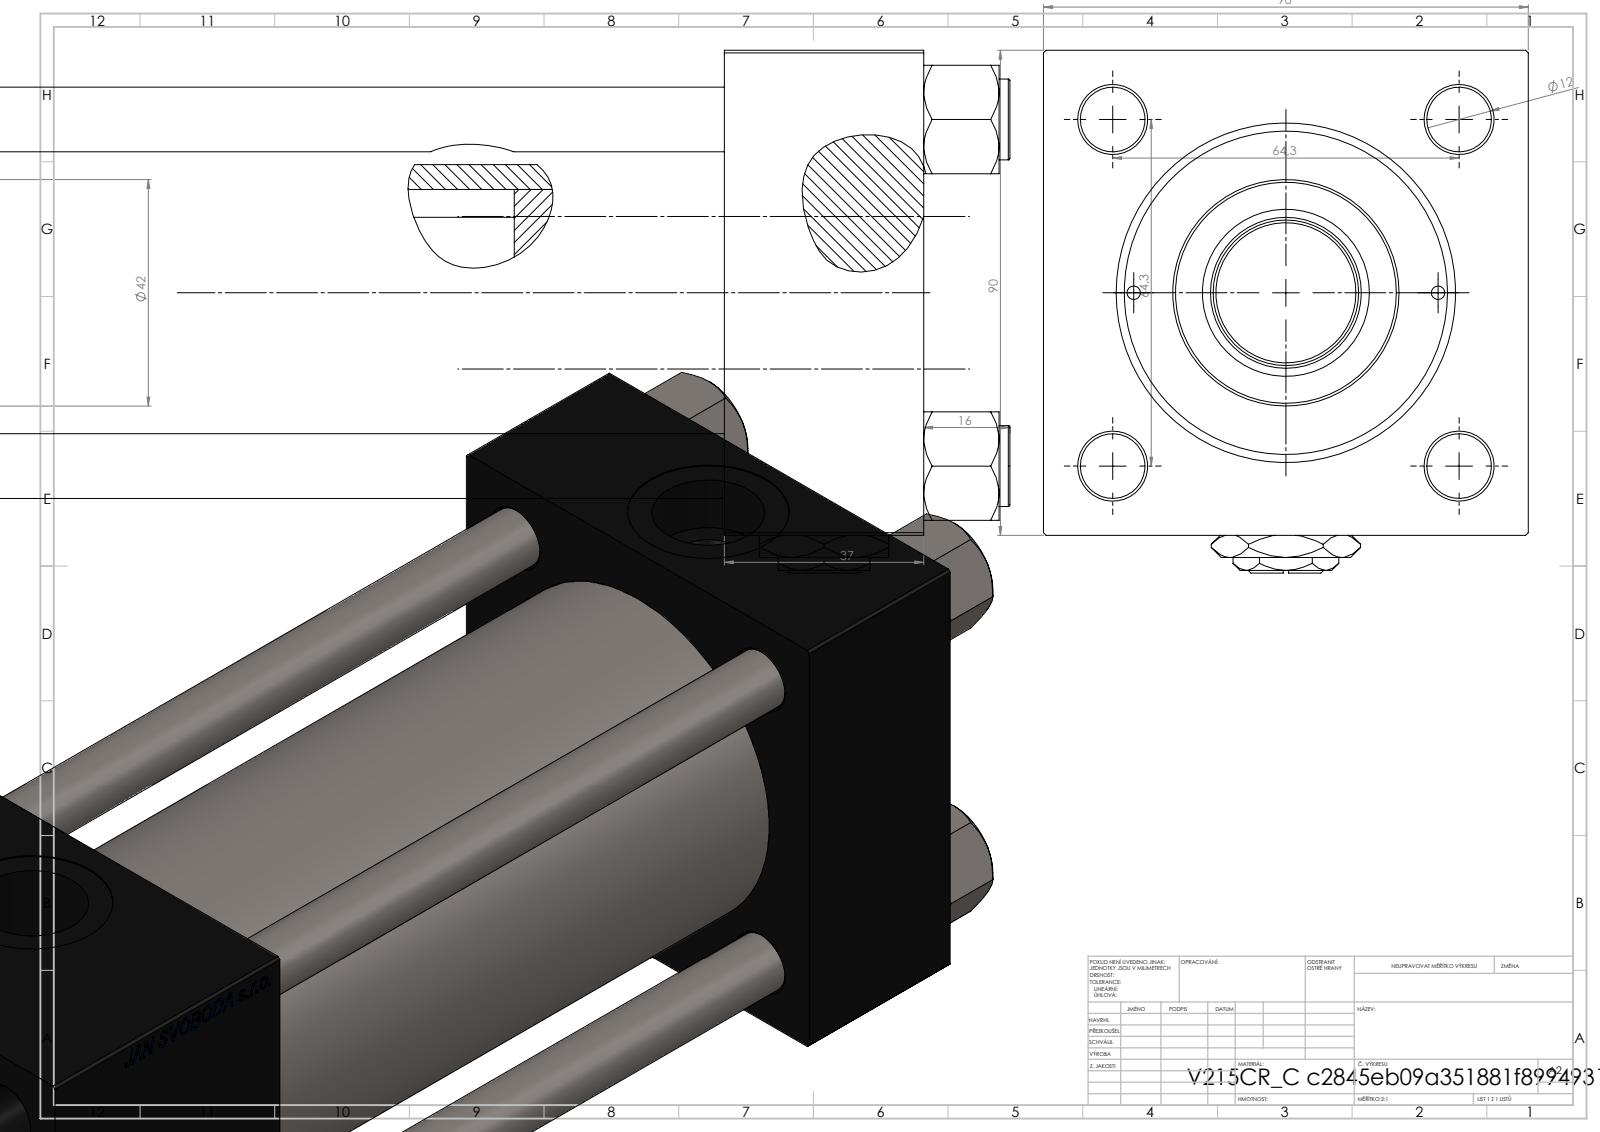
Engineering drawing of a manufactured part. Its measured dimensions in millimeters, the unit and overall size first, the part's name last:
Units: millimetres
Overall size (bounding box): 311 × 97 × 90
Round holes (diameter × count): ⌀12 ×4, ⌀2.5 ×2, ⌀7 ×2, ⌀20.96 ×2, ⌀30 ×2, ⌀18.5 ×1, ⌀28 ×1, ⌀31 ×1, ⌀50 ×1, ⌀60 ×1, ⌀63 ×1
Round bosses / shafts (diameter × count): ⌀15 ×4, ⌀69 ×1, ⌀42 ×1, ⌀27 ×1, ⌀18 ×1
Main face-to-face distances: 90, 37, 198, 235, 59, 176, 139, 206.3, 169.3, 30.3
Hole centre spacings: 32.39, 45.47, 64.3, 68.42, 28.25, 90.93, 56.5, 177.5
Volume: 1 087 000 mm³ · Surface area: 239 643 mm²
Bodies: 14 solids, 1270 faces (580 planar, 106 cylindrical, 584 other)
Part name (STEP PRODUCT): Zatka_pro_OIL_PORT; V215CR_C_Body; V215_VC_A; V215CR_ROD_END_F (+3 more)
STEP written by: SolidWorks 2019 (CONFIG_CONTROL_DESIGN)
